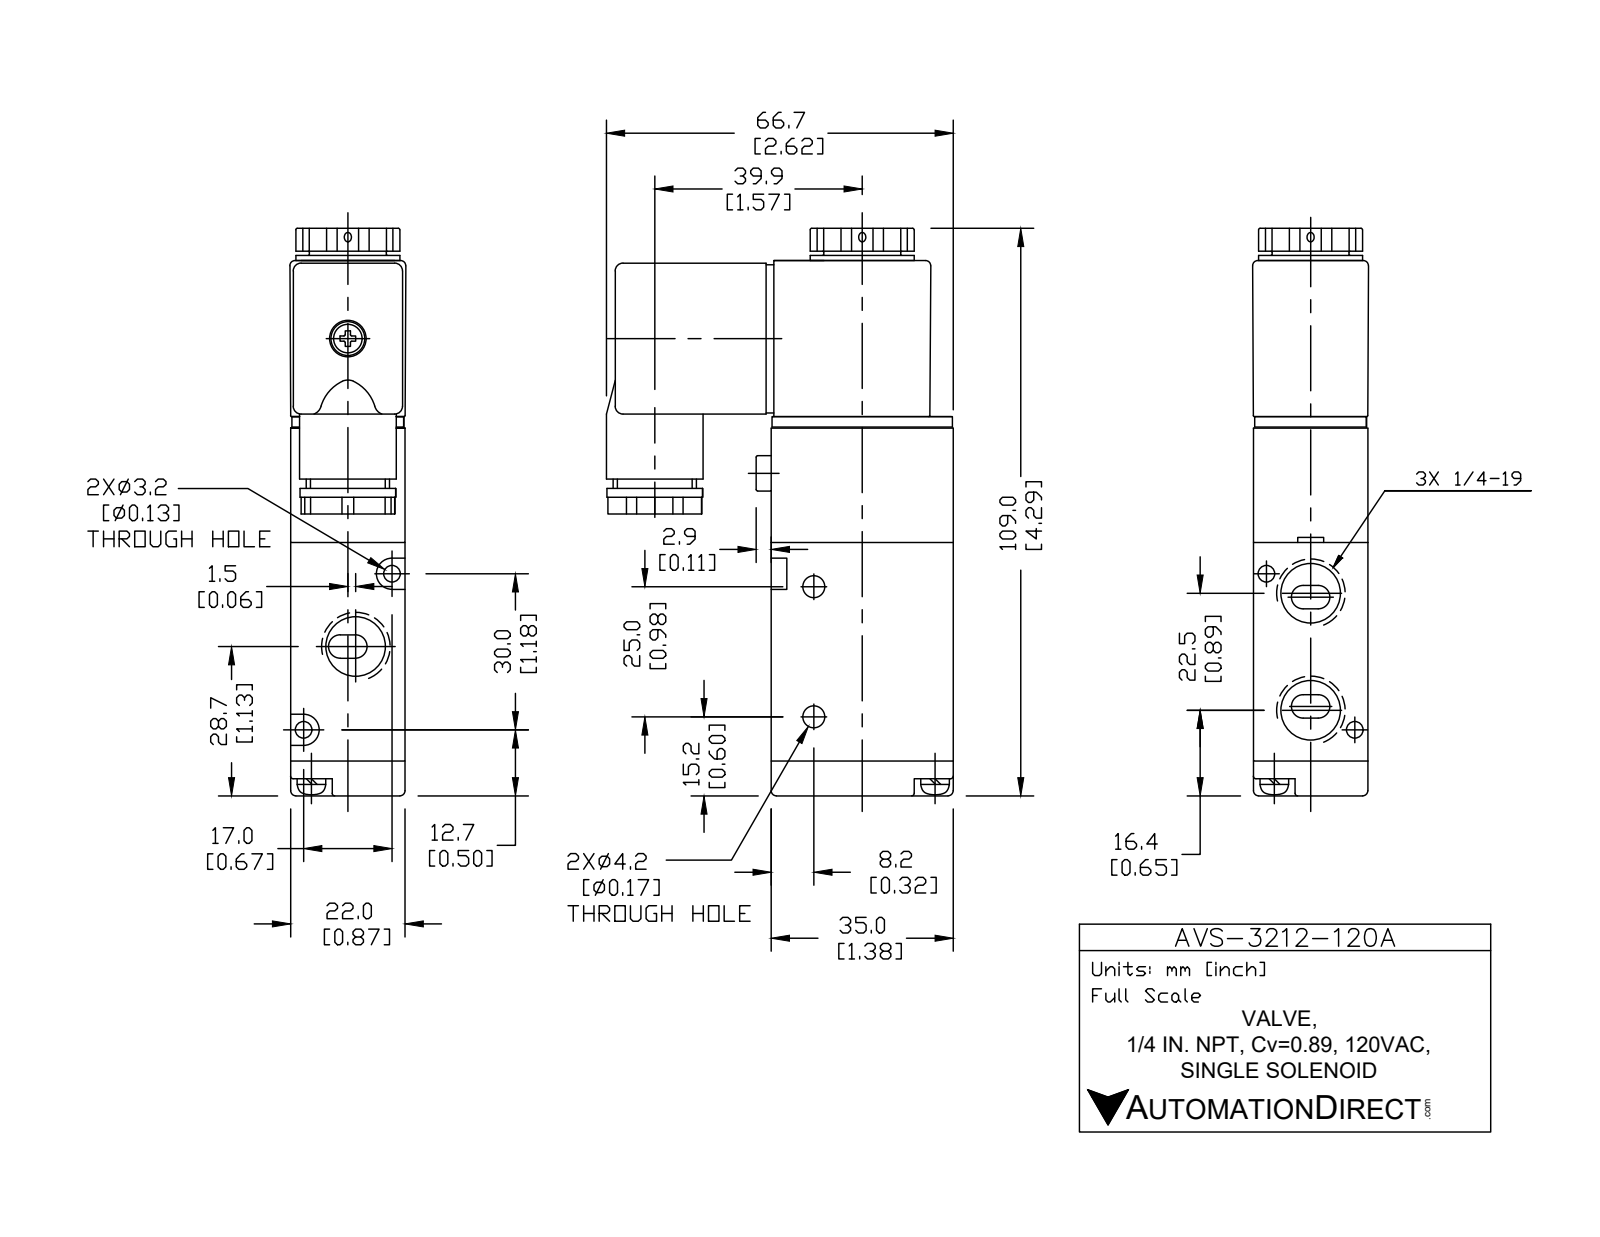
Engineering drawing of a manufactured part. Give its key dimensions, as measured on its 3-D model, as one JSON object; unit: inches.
{"part_name": "AVS-3212-120A", "step_written_by": "SolidWorks 2015 (CONFIG_CONTROL_DESIGN)", "units": "inches", "bodies": {"solids": 4, "faces": 159, "planar": 84, "cylindrical": 53, "other": 22}, "overall_size": [4.295, 2.626, 0.866], "volume_in3": 5.733, "surface_area_in2": 36.97, "round_holes": [[0.438, 3], [0.169, 2], [0.126, 1], [0.13, 1], [0.366, 1]], "round_bosses_or_shafts": [[0.787, 1], [0.732, 1], [0.724, 1], [0.63, 1], [0.583, 1], [0.268, 1]], "partial_cylinders_radius": [[0.02, 11], [0.039, 10], [0.118, 2]], "face_to_face_distances": [0.02, 0.846, 1.654, 0.866, 0.264, 1.917, 4.031, 0.827, 1.181, 3.768], "hole_center_spacings": [0.365, 0.367, 0.41, 0.484, 0.616, 0.743, 0.886, 0.984]}
